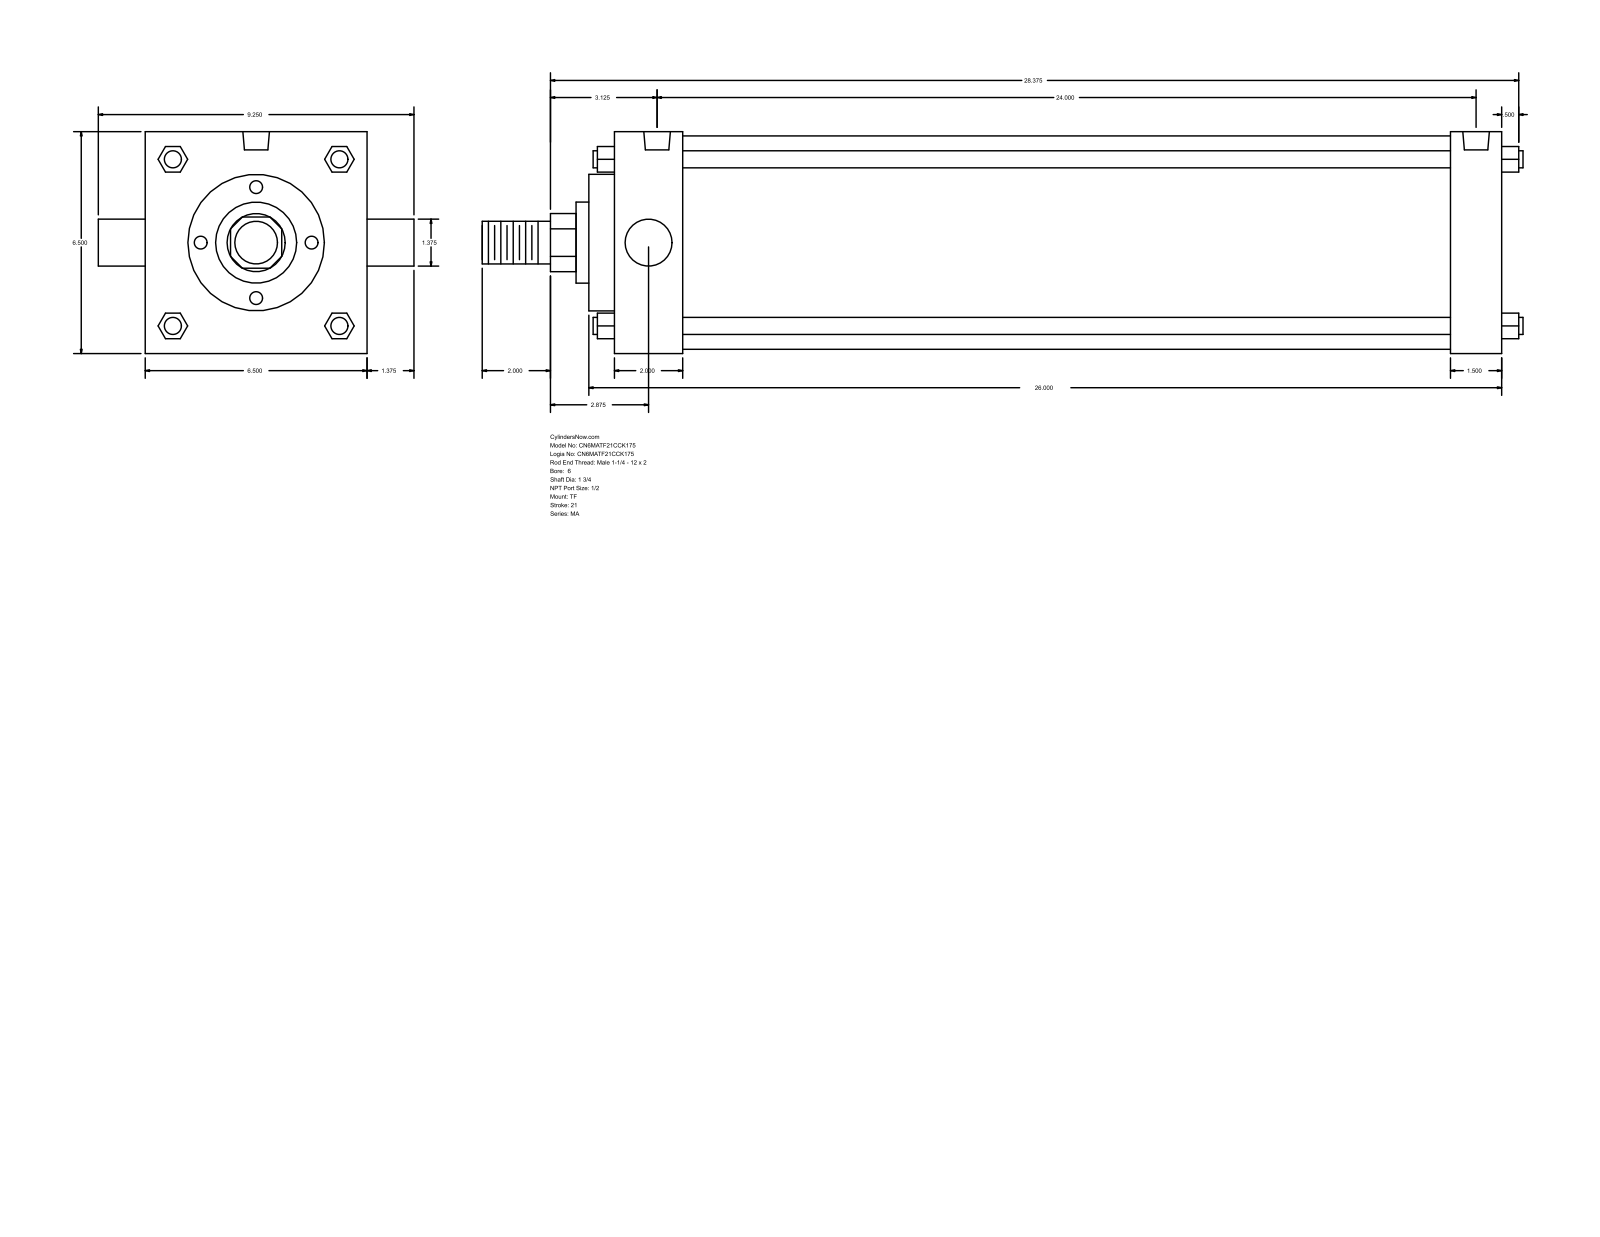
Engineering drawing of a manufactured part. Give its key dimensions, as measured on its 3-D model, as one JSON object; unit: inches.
{"part_name": "MA_TF__0600_1.75", "step_written_by": "GSSL Pune (CONFIG_CONTROL_DESIGN)", "units": "inches", "bodies": {"solids": 0, "faces": 122, "planar": 93, "cylindrical": 29, "other": 0}, "overall_size": [30.5, 9.25, 6.5], "round_holes": [[0.687, 3], [0.778, 2]], "round_bosses_or_shafts": [[0.5, 4], [6.25, 1], [4, 1], [2.375, 1], [1.75, 1], [1.375, 1], [1.25, 1]], "partial_cylinders_radius": [[0.852, 1]], "face_to_face_distances": [6.5, 26, 0.75, 1.5, 2, 24, 24.5, 22.5, 2.75, 25.25], "hole_center_spacings": [24]}
